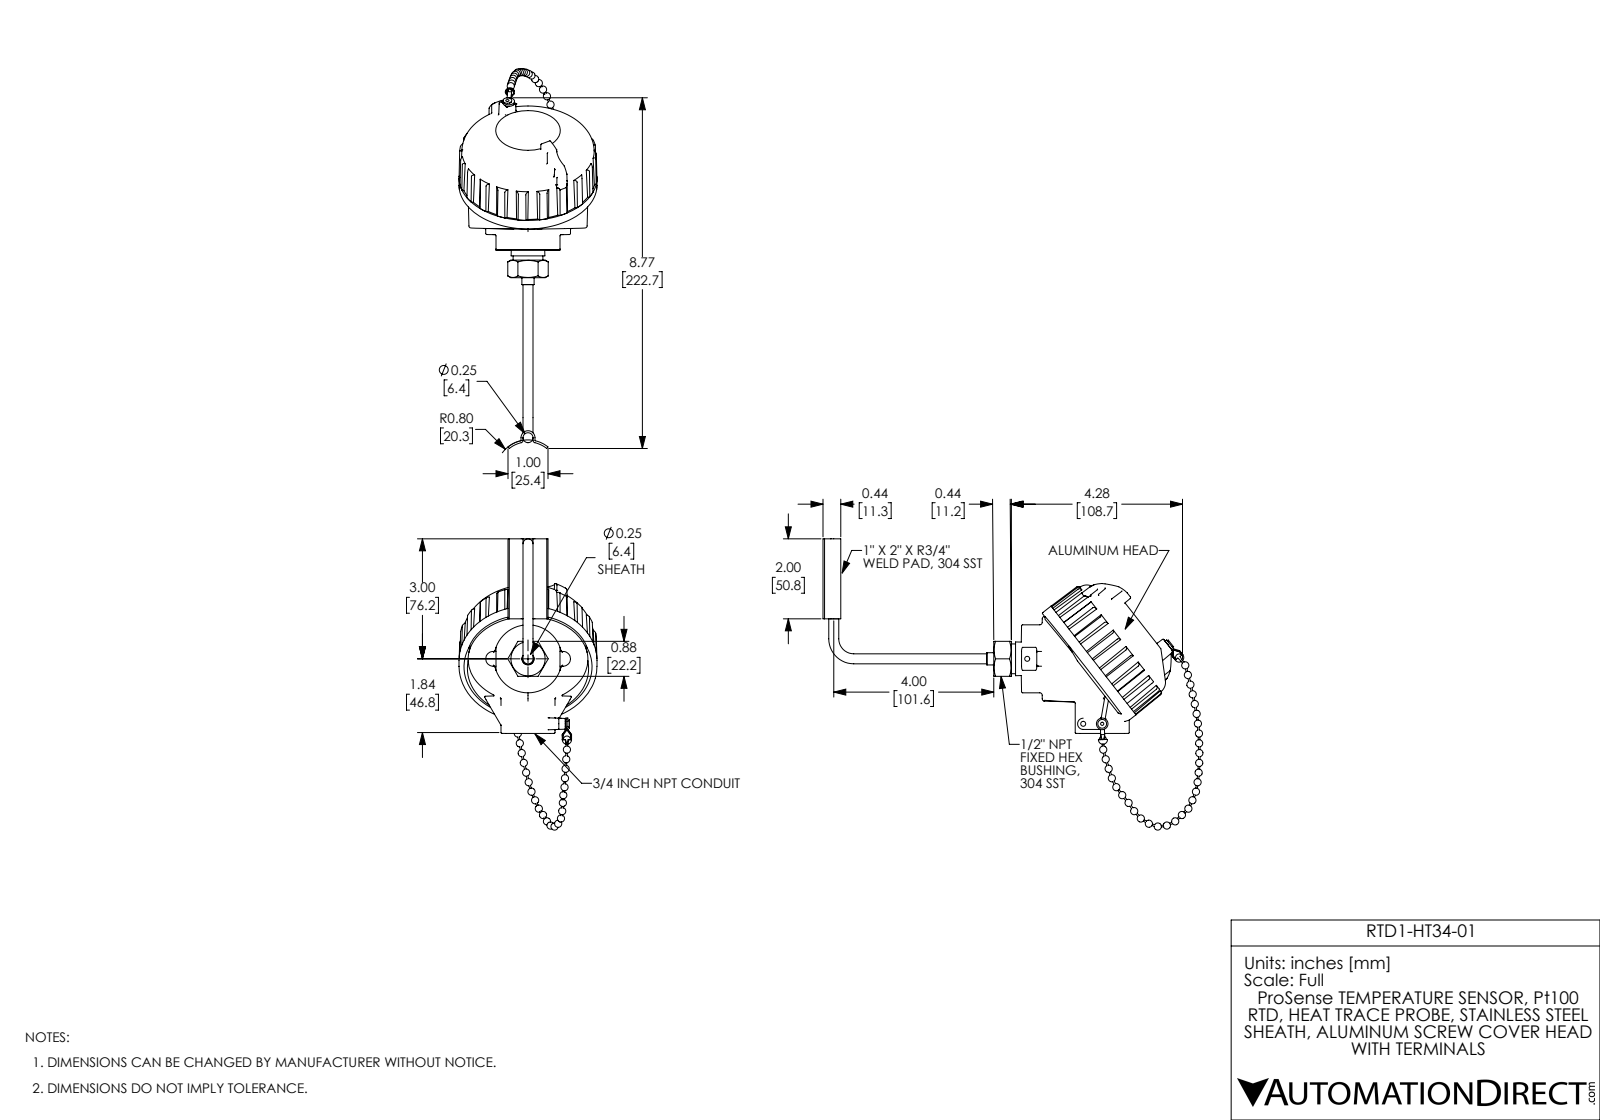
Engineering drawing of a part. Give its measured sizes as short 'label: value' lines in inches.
name: RTD1-HT34-01
written by: SolidWorks 2017 (AUTOMOTIVE_DESIGN)
unit: in
bodies: 73 solids, 738 faces (231 planar, 149 cylindrical, 358 other)
size: 9.499 × 7.283 × 3.45
volume: 21.26 in³; area: 74.14 in²
holes: 2× ⌀0.08, 2× ⌀0.125, 2× ⌀0.144, 1× ⌀0.165, 1× ⌀0.25, 1× ⌀0.437, 1× ⌀0.688
bosses: 31× ⌀0.04, 2× ⌀0.29, 2× ⌀0.123, 1× ⌀3.45, 1× ⌀1.7, 1× ⌀1.35, 1× ⌀0.745, 1× ⌀0.305
rounds: 11× R0.03, 8× R0.02, 6× R0.015, 2× R0.01, 2× R0.06, 2× R0.185, 1× R0.175, 1× R0.75
face distances: 1.792, 0.875, 1.336, 0.675, 0.05, 0.925, 0.625, 0.975, 0.3, 0.025
hole spacings: 0.033, 0.475, 2.145, 2.481
